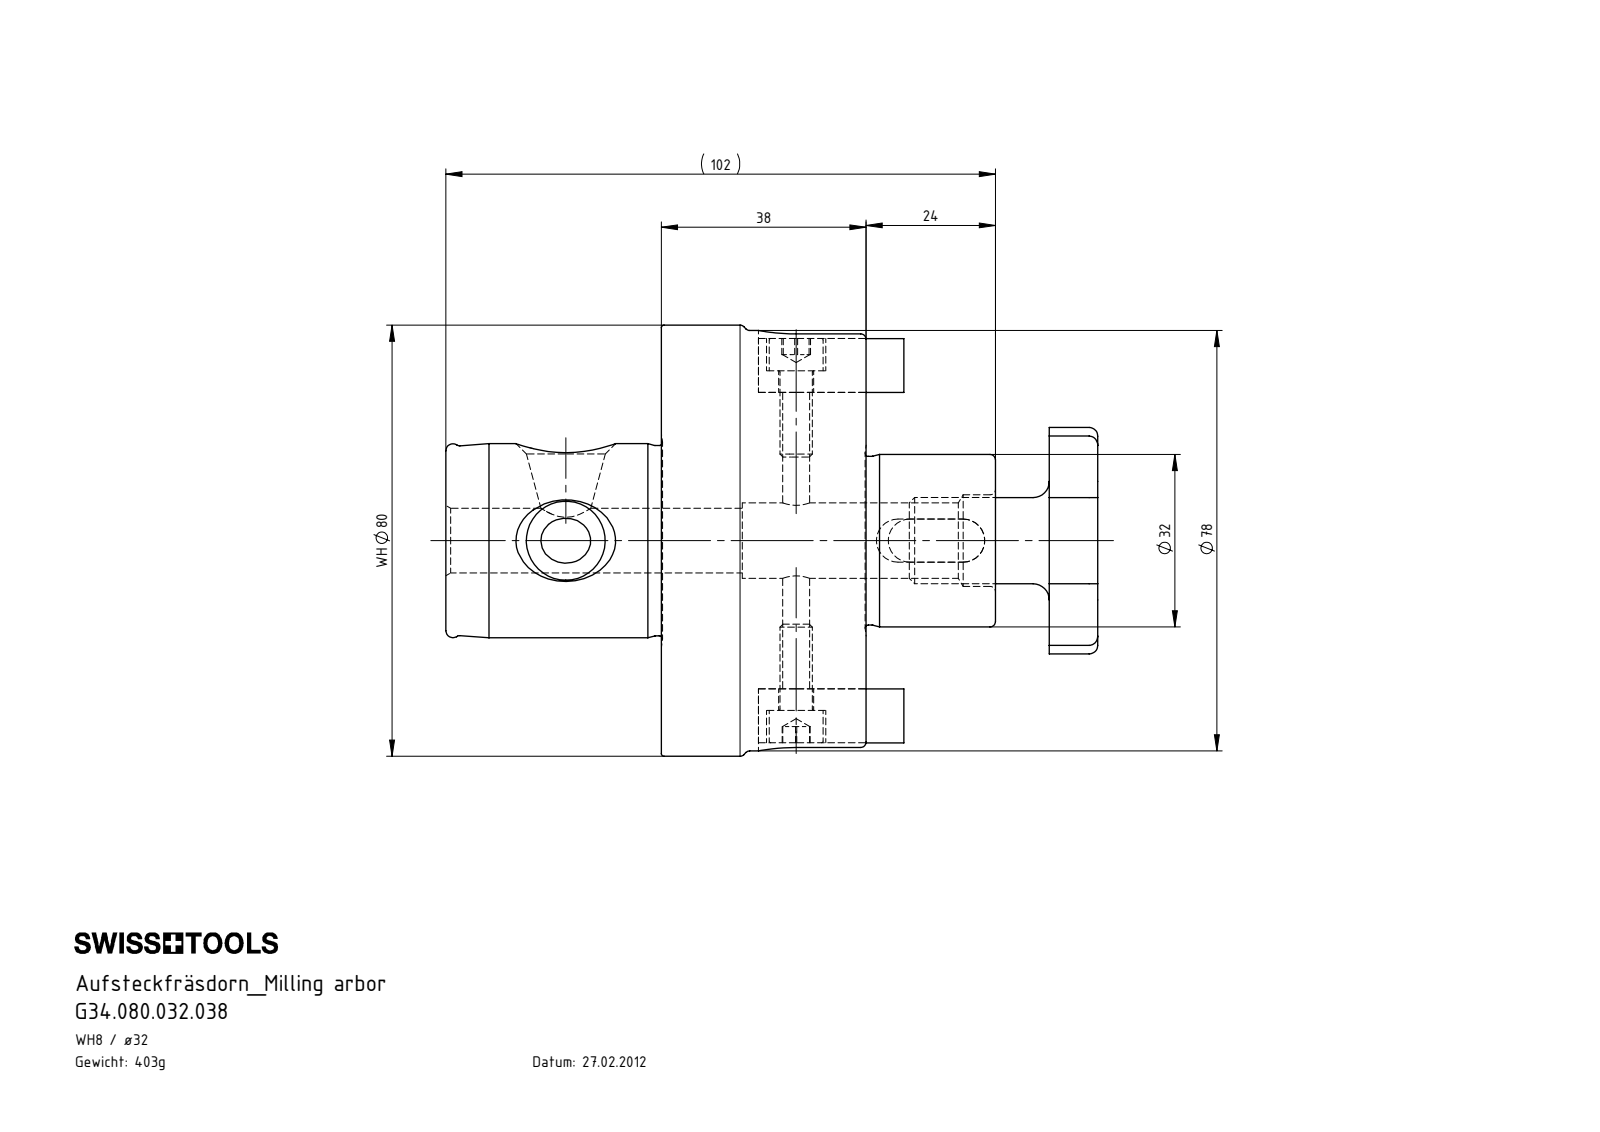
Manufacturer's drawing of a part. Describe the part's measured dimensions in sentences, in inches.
The part is named "D32-ER2.002.014_A; ISO 4762 - M6 x 16; WH8.D32.001.038; WH8-D32.001.038_A (+2 more)". Its 3-D file was written by "SolidWorks 2022 (AUTOMOTIVE_DESIGN)". It is 7 solids with 208 faces: 71 planar, 60 cylindrical and 77 other. Overall it measures 4.764 by 3.15 by 3.15 inches. Its volume is 14.88 cubic inches and its surface area 64.94 square inches. Round holes: 1 of diameter 0.197, 1 of diameter 0.256, 1 of diameter 0.433, 1 of diameter 0.472, 1 of diameter 0.551, 1 of diameter 0.669. Round bosses or shafts: 1 of diameter 3.15, 1 of diameter 3.071, 1 of diameter 1.417, 1 of diameter 1.39, 1 of diameter 1.26, 1 of diameter 1.232, 1 of diameter 0.63, 1 of diameter 0.394. Partial cylindrical surfaces (rounded edges, fillets, slot ends): 4 of radius 0.118, 3 of radius 0.157, 1 of radius 0.276, 1 of radius 0.827. The main face-to-face distances are 1.496, 0.394, 1.693, 3.189, 1.575, 3.071, 4.764, 2.835, 4.409, 1.339.
